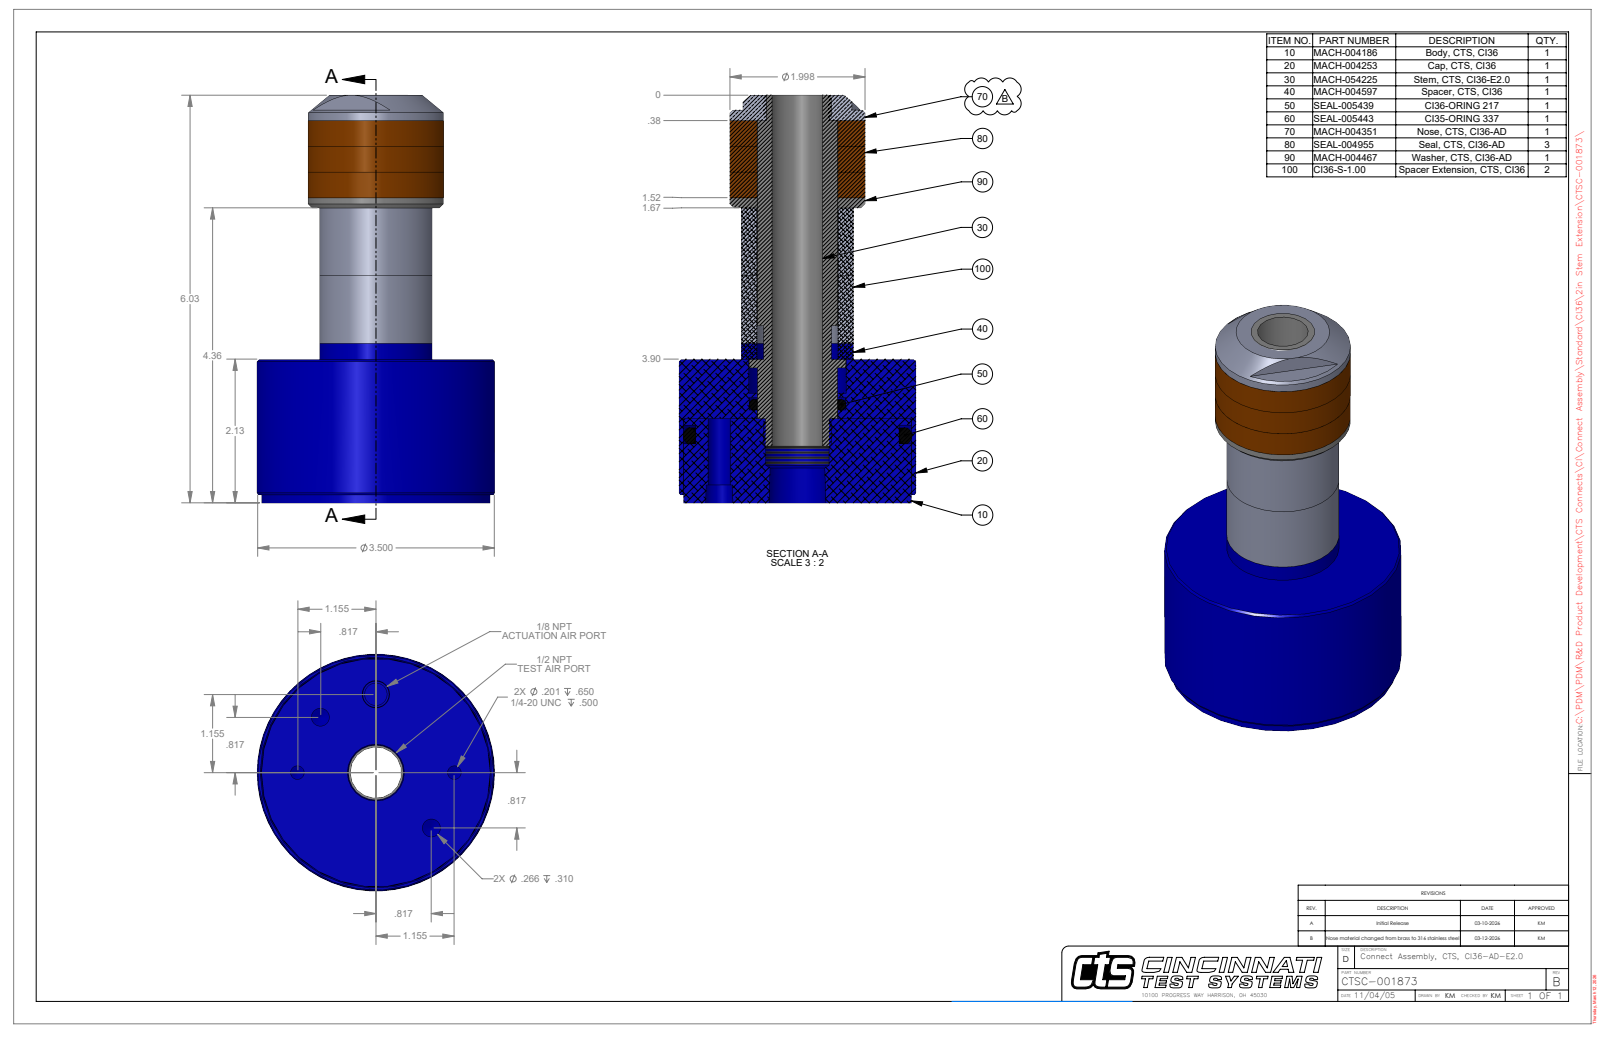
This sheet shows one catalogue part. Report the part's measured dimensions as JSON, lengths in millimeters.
{"part_name": "CTSC-001873", "step_written_by": "SolidWorks 2023 (AUTOMOTIVE_DESIGN)", "units": "millimeters", "bodies": {"solids": 9, "faces": 80, "planar": 38, "cylindrical": 29, "other": 13}, "overall_size": [153.21, 88.9, 88.9], "volume_mm3": 445509, "surface_area_mm2": 87477, "round_holes": [[5.11, 2], [6.75, 2], [19.05, 1], [23.42, 1], [23.81, 1], [30.35, 1], [30.35, 1], [30.43, 1], [36.53, 1], [85.67, 1]], "round_bosses_or_shafts": [[88.9, 1], [85.47, 1], [50.75, 1], [42.06, 1], [36.25, 1], [30.12, 1], [25.4, 1]], "face_to_face_distances": [9.65, 53.97, 143.56, 89.59, 25.4, 19.3, 133.91, 79.94, 114.6, 124.26], "hole_center_spacings": [22.45, 29.33, 29.34, 54.2, 58.66, 58.68]}
